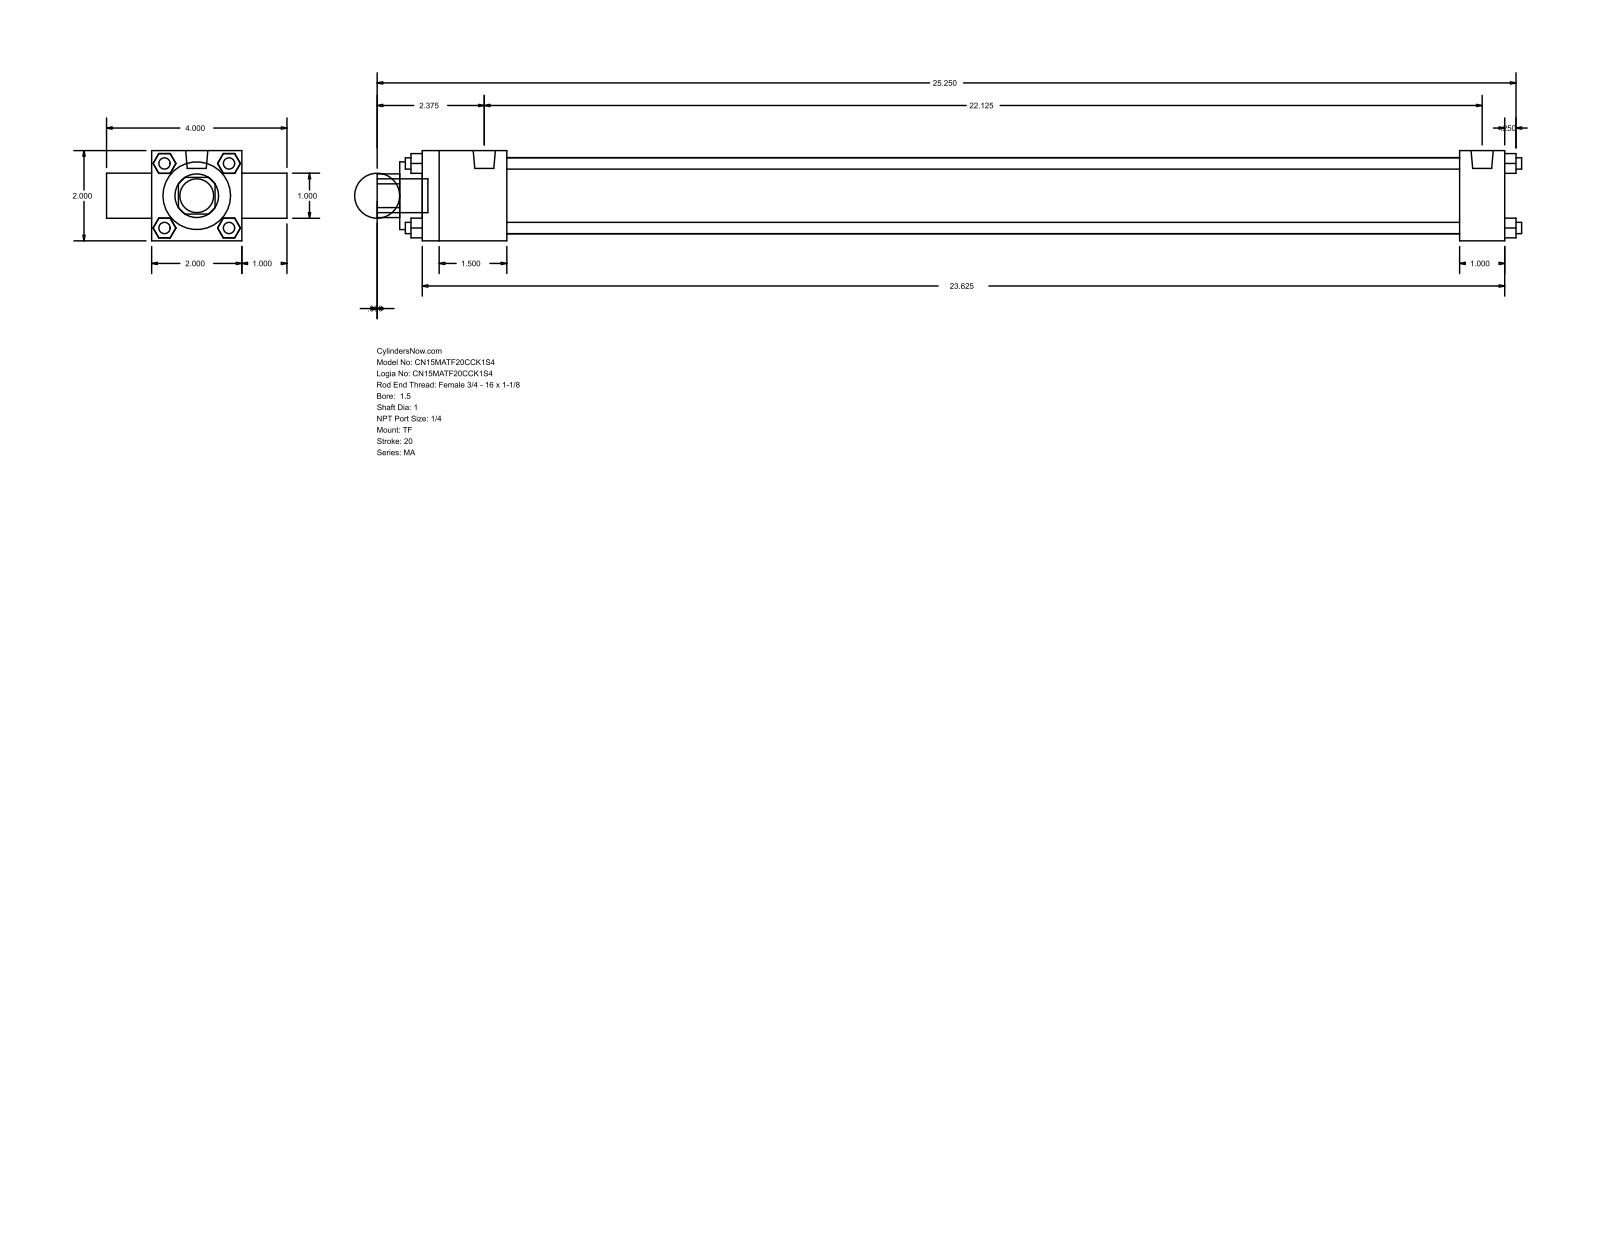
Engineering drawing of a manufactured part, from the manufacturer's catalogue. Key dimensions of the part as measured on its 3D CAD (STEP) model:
Part name (STEP PRODUCT): MA_TF__0150_1
STEP written by: GSSL Pune (CONFIG_CONTROL_DESIGN)
Units: millimetres
Bodies: 0 solids, 120 faces (92 planar, 28 cylindrical, 0 other)
Overall size (bounding box): 644.52 × 101.6 × 50.8
Round holes (diameter × count): ⌀25.4 ×2, ⌀38.1 ×1, ⌀42.93 ×1
Round bosses / shafts (diameter × count): ⌀6.35 ×4, ⌀7.94 ×3, ⌀12.49 ×2, ⌀19.05 ×1
Partial cylindrical surfaces — rounded edges, fillets, slot ends (radius × count): R12.29 ×1
Main face-to-face distances: 50.8, 25.4, 609.6, 76.2, 6.35, 47.63, 584.2, 536.57, 561.97, 622.3
